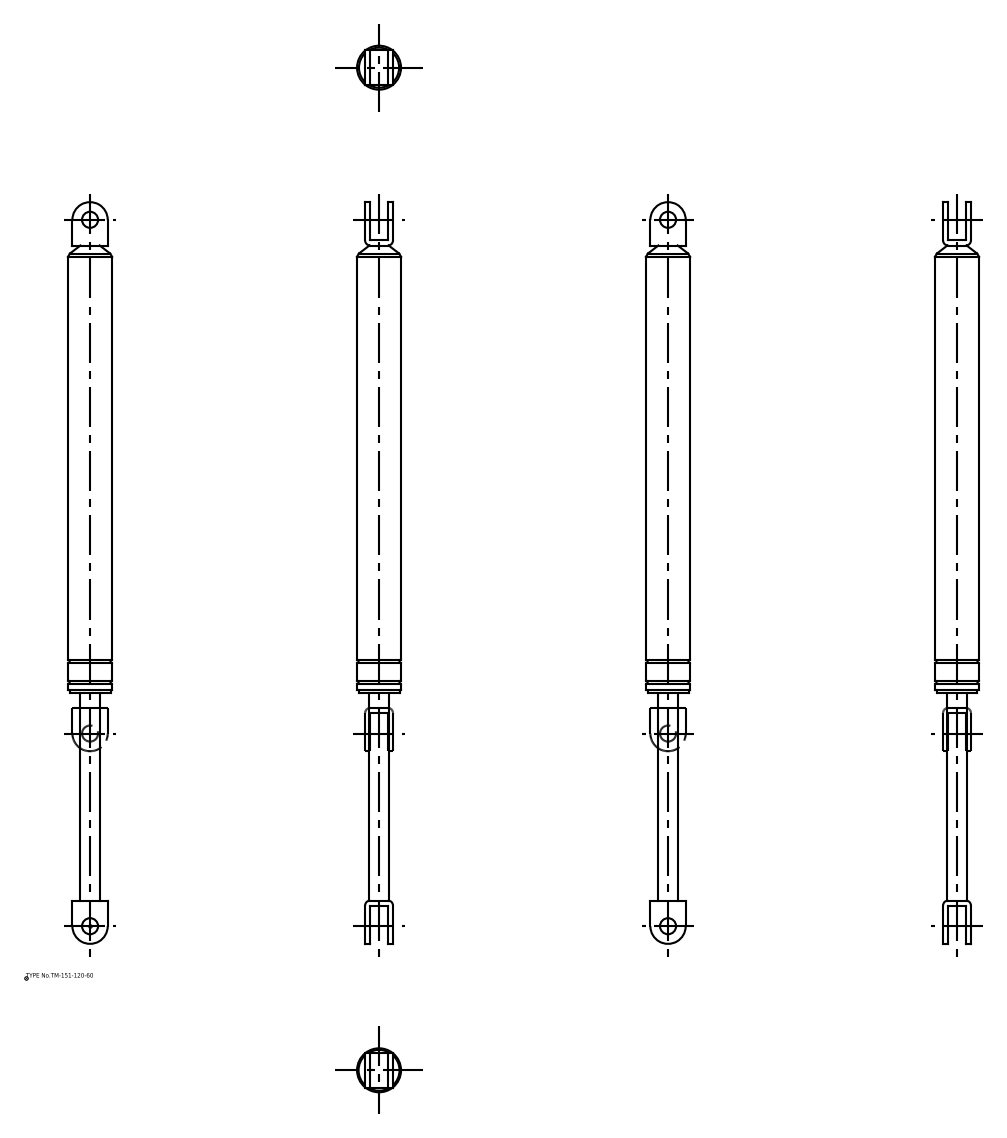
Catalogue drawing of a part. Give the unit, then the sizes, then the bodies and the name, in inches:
Units: inches
Overall size (bounding box): 18.189 × 1.11 × 1.11
Round holes (diameter × count): ⌀0.394 ×2
Round bosses / shafts (diameter × count): ⌀1.11 ×1, ⌀1.079 ×1, ⌀1.004 ×1, ⌀0.492 ×1
Partial cylindrical surfaces — rounded edges, fillets, slot ends (radius × count): R0.126 ×4, R0.433 ×2
Main face-to-face distances: 0.126, 0.559, 0.685, 0.433, 0.866, 16.189, 5.205, 16.315, 11.11, 10.984
Hole centre spacings: 17.323
Volume: 11.35 in³ · Surface area: 55.59 in²
Bodies: 2 solids, 64 faces (22 planar, 32 cylindrical, 10 other)
Part name (STEP PRODUCT): TM_151_120_60; TM_151_120_60_div
STEP written by: spGate 16.7.1 (AUTOMOTIVE_DESIGN)
